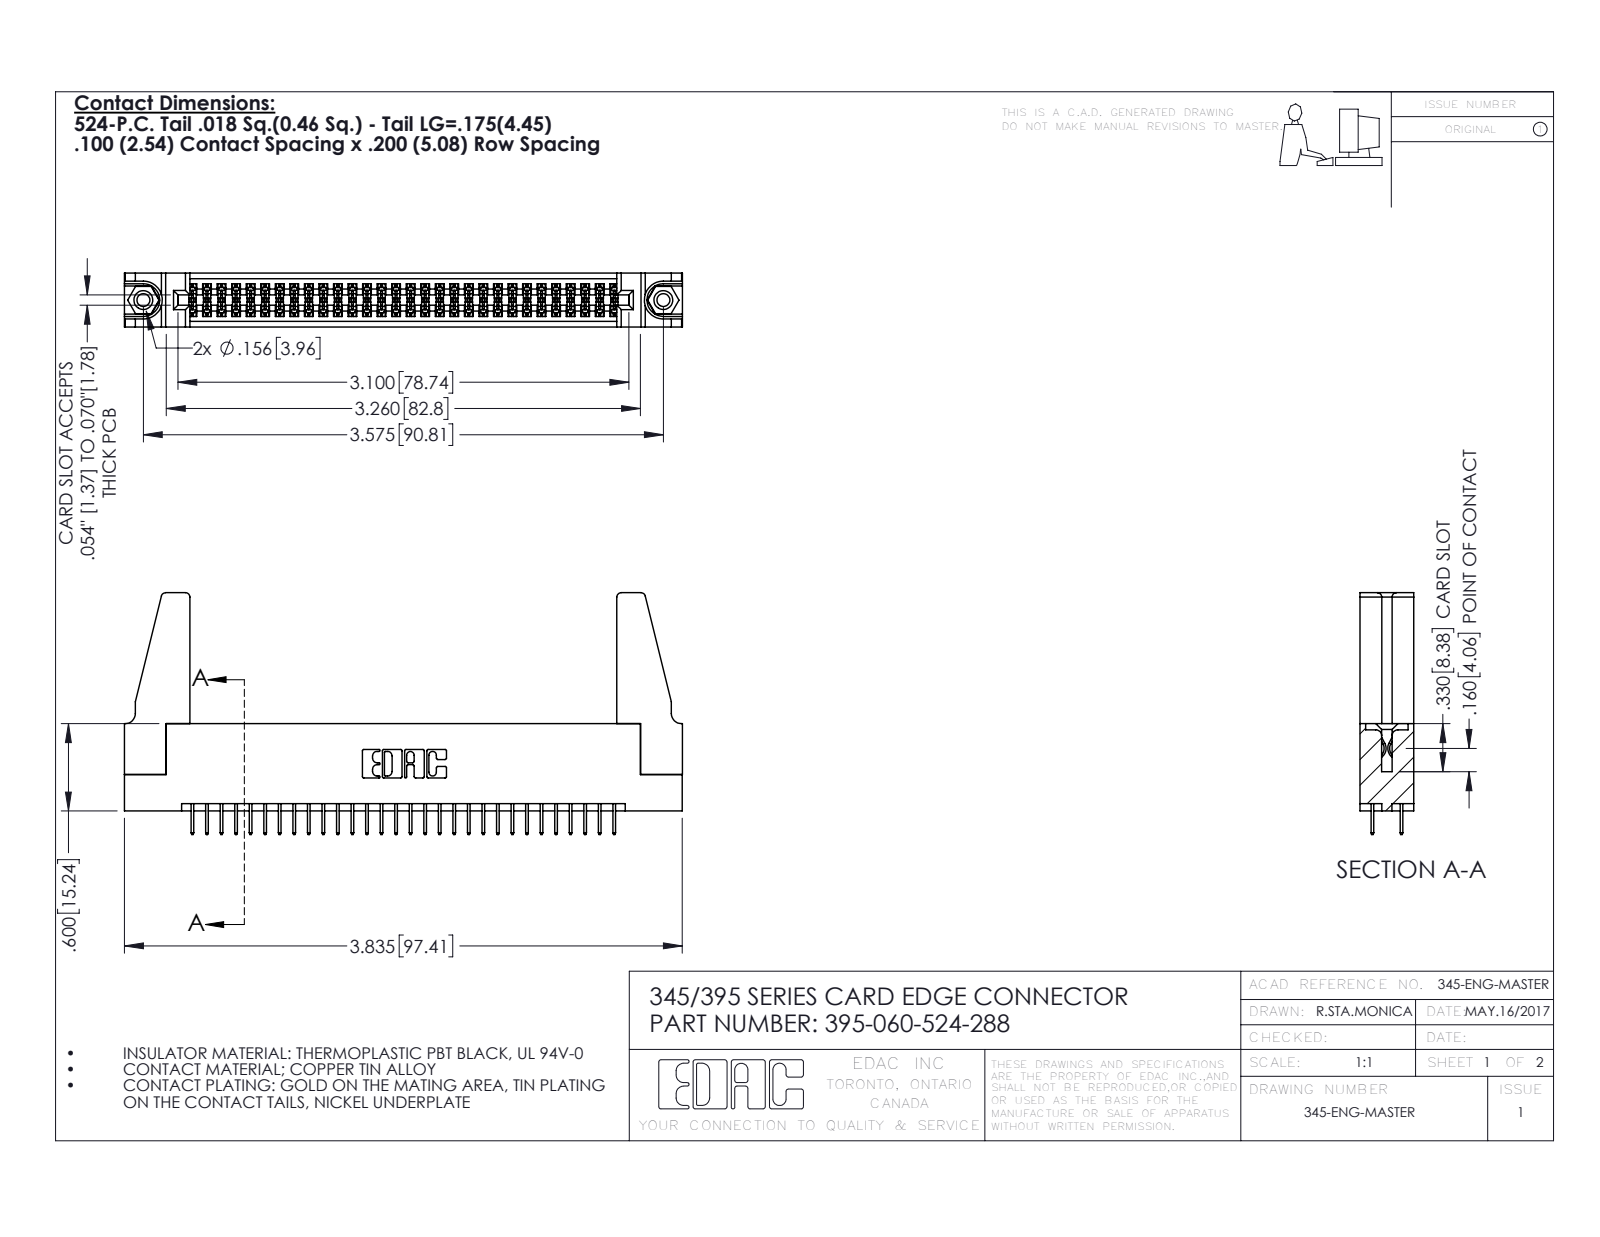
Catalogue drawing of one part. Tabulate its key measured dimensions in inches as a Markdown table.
| quantity | value |
| --- | --- |
| part name | 395-060-524-288; 345 Part_Flush Mounting Lugs - 0.156 Dia-TH; 345-220-078_345-220-088; 345-292-001_345-293-124 (+1 more) |
| STEP written by | SolidWorks 2016 (CONFIG_CONTROL_DESIGN) |
| units | inches |
| bodies | 65 solids, 3490 faces (2492 planar, 982 cylindrical, 16 other) |
| overall size | 3.836 × 1.662 × 0.37 |
| volume | 0.764 in³ |
| surface area | 25.33 in² |
| round holes (diameter × count) | 0.089 × 2, 0.125 × 2, 0.156 × 2, 0.064 × 1 |
| round bosses / shafts (diameter × count) | 0.155 × 2 |
| partial cylindrical surfaces (radius × count) | 0.006 × 90, 0.01 × 22, 0.03 × 8, 0.007 × 6, 0.031 × 6, 0.026 × 3, 0.014 × 2, 0.019 × 2 |
| main face-to-face distances | 0.072, 0.298, 0.37, 0.2, 0.098, 0.272, 0.025, 0.225, 0.072, 0.175 |
| hole center spacings | 0.27, 3.34, 3.575 |
